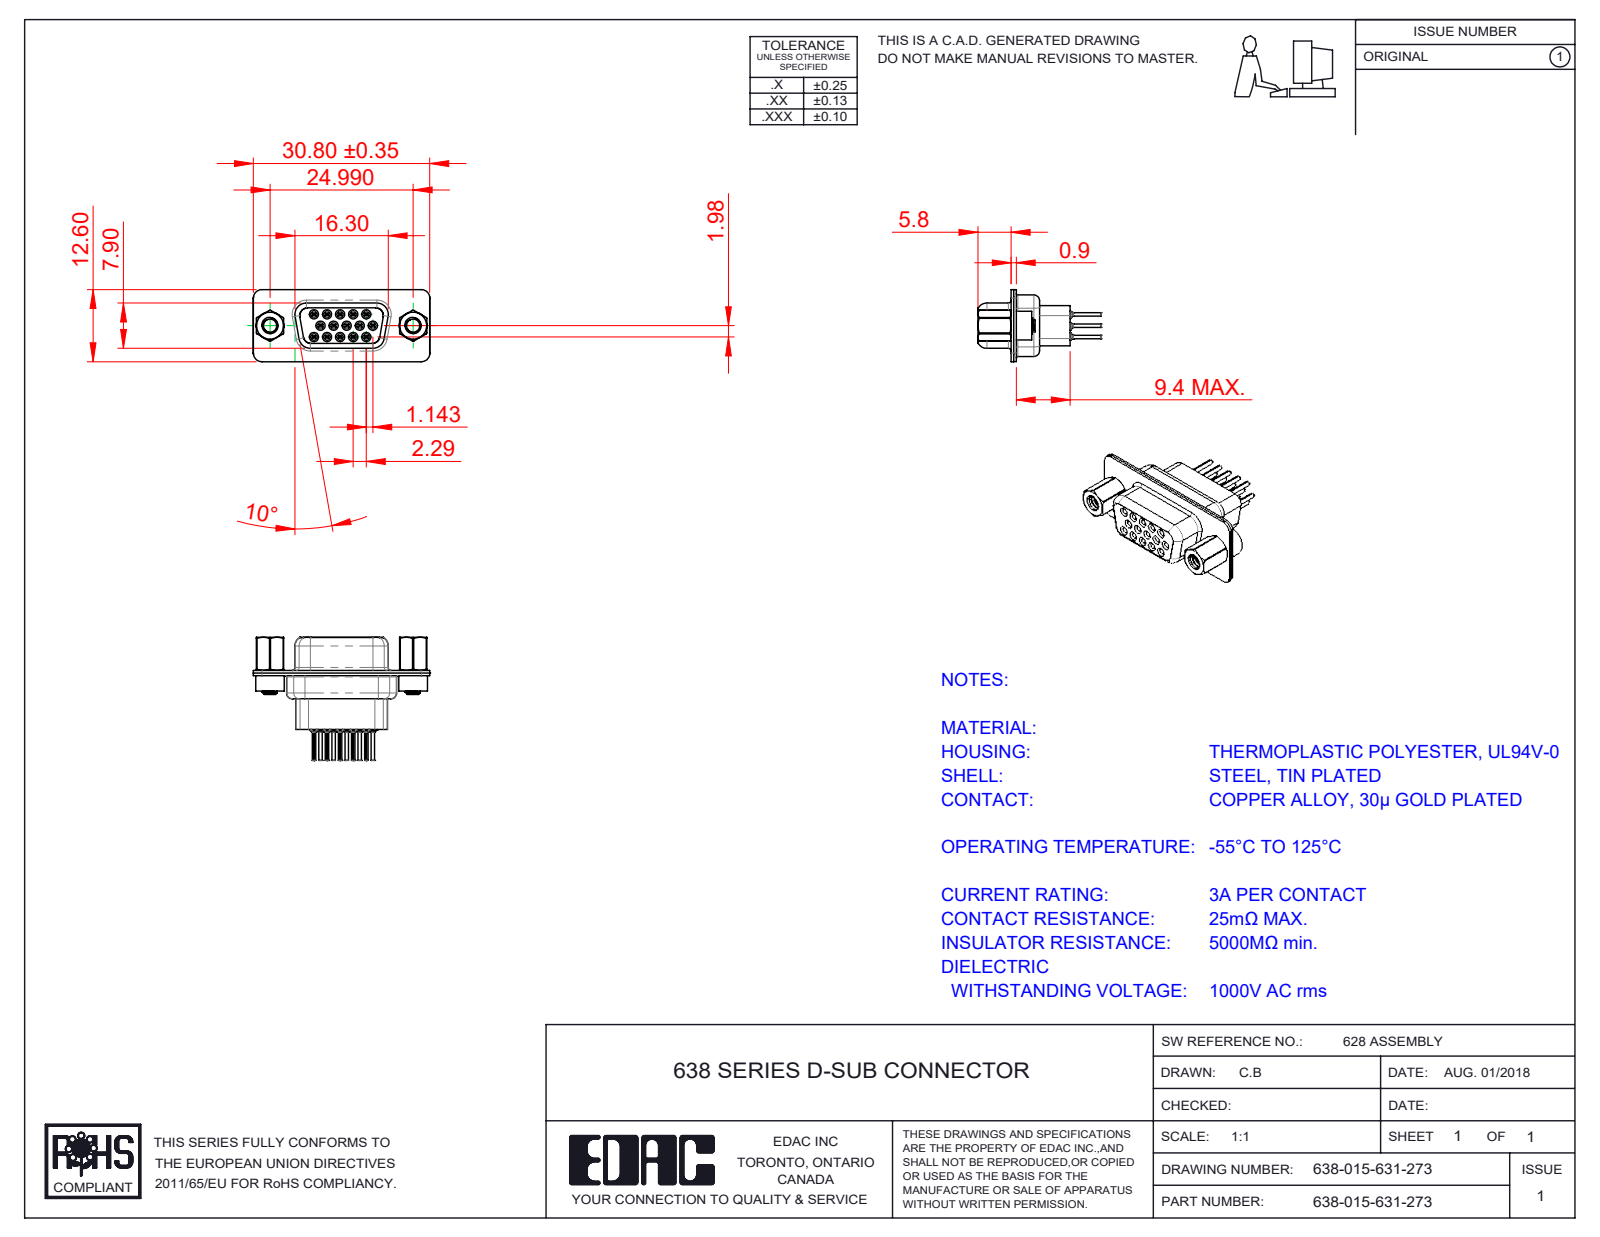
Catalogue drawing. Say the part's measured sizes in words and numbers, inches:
The part is named "638 Housing_15 Contacts HP; 638 Shell Front_15 Contacts; 638 Shell Rear_15 Contacts; 638 Contact Row 3_31 (+5 more)". Its 3-D file was written by "SolidWorks 2020 (CONFIG_CONTROL_DESIGN)". It is 22 solids with 2250 faces: 554 planar, 704 cylindrical and 992 other. Overall it measures 1.213 by 0.846 by 0.496 inches. Its volume is 0.128 cubic inches and its surface area 10.87 square inches. Round holes: 15 of diameter 0.008, 15 of diameter 0.031, 15 of diameter 0.039, 15 of diameter 0.043, 15 of diameter 0.063, 15 of diameter 0.067, 15 of diameter 0.071, 2 of diameter 0.079, 2 of diameter 0.089, 2 of diameter 0.09, 2 of diameter 0.157, 2 of diameter 0.159. Round bosses or shafts: 15 of diameter 0.079, 15 of diameter 0.059, 15 of diameter 0.047, 15 of diameter 0.024, 2 of diameter 0.197, 2 of diameter 0.195, 2 of diameter 0.189, 2 of diameter 0.11. Partial cylindrical surfaces (rounded edges, fillets, slot ends): 30 of radius 0.004, 20 of radius 0.059, 12 of radius 0.079, 10 of radius 0.011, 8 of radius 0.061, 5 of radius 0.053, 4 of radius 0.01, 4 of radius 0.02. The main face-to-face distances are 0.018, 0.035, 0.016, 0.056, 0.35, 0.26, 0.276, 0.228, 0.09, 0.37. The hole center spacings are 0.156, 0.09, 0.18, 0.09, 0.238, 0.238, 0.27, 0.312.
